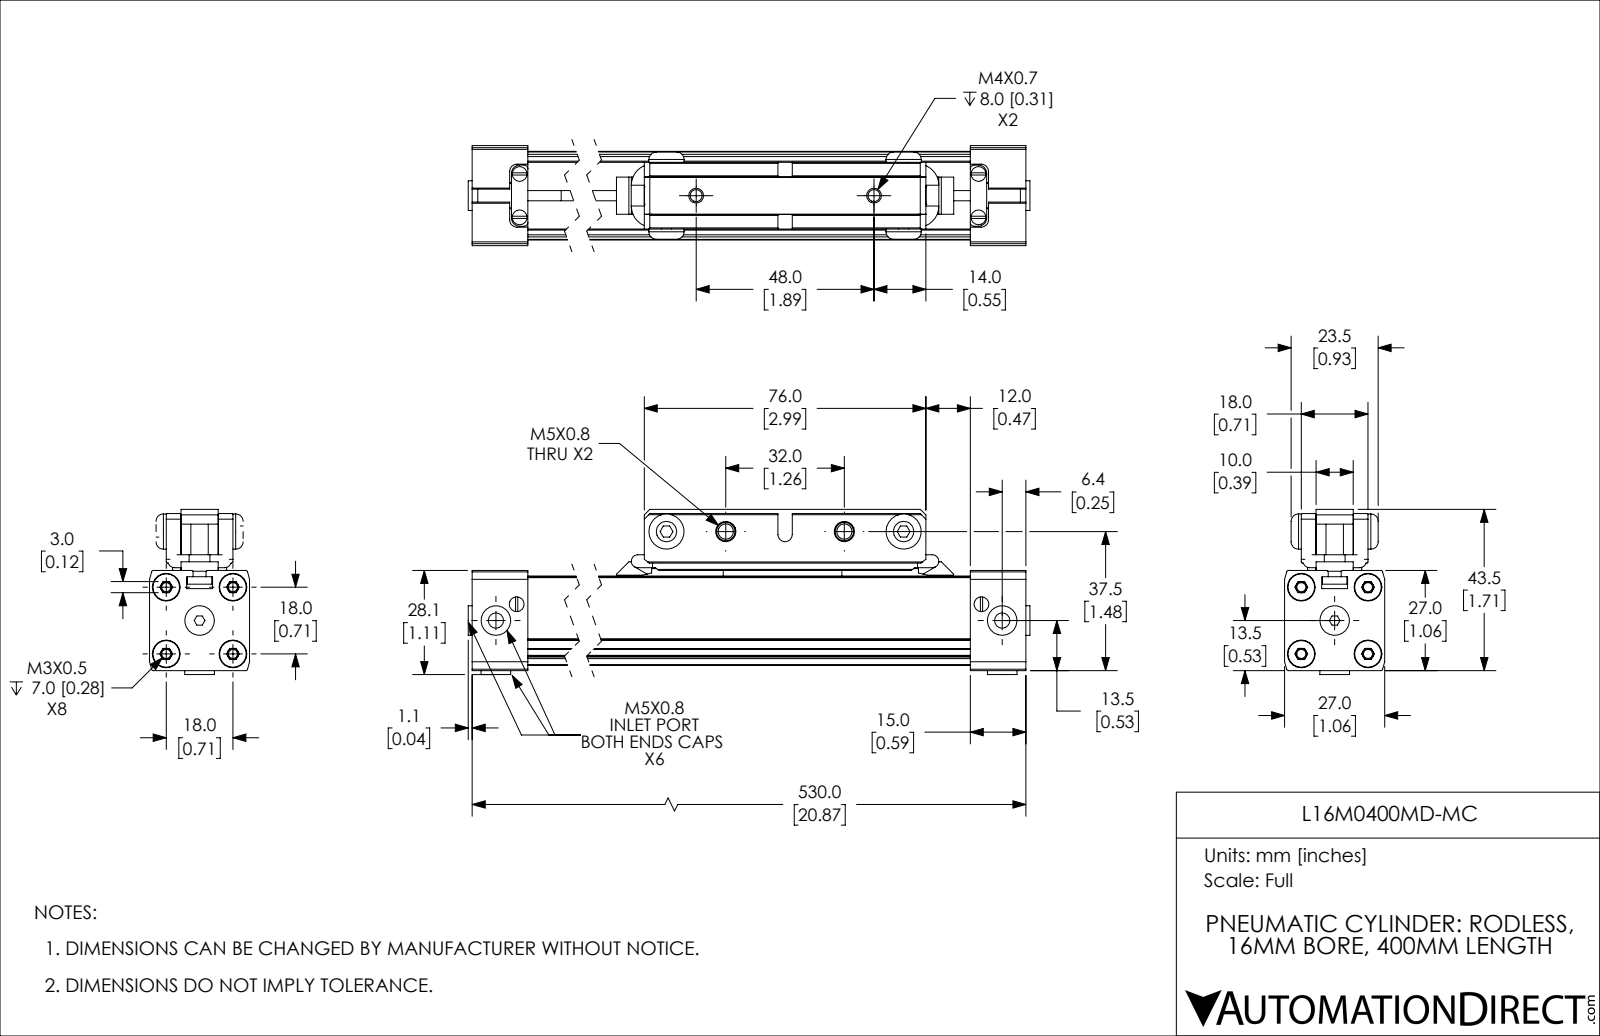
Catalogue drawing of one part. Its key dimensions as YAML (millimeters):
part_name: "L16M0400MD-MC_PISTON; L16M0400MD-MC; L16M0400MD-MC_BODY"
step_written_by: "SolidWorks 2019 (CONFIG_CONTROL_DESIGN)"
units: millimeters
bodies: {solids: 13, faces: 827, planar: 435, cylindrical: 284, other: 108}
overall_size: [532.15, 44.57, 27]
volume: 223973
surface_area: 116095
round_holes:
  - {diameter: 4.13, count: 9}
  - {diameter: 4, count: 6}
  - {diameter: 8, count: 5}
  - {diameter: 2.46, count: 4}
  - {diameter: 5.5, count: 4}
  - {diameter: 7.5, count: 4}
  - {diameter: 3.24, count: 2}
  - {diameter: 16.1, count: 1}
round_bosses_or_shafts:
  - {diameter: 7.2, count: 4}
  - {diameter: 3.5, count: 4}
  - {diameter: 5, count: 3}
  - {diameter: 3.8, count: 3}
  - {diameter: 9.5, count: 2}
  - {diameter: 16, count: 1}
partial_cylinders:
  - {radius: 0.3, count: 22}
  - {radius: 0.5, count: 14}
  - {radius: 0.25, count: 8}
  - {radius: 0.62, count: 6}
  - {radius: 1, count: 6}
  - {radius: 0.2, count: 4}
  - {radius: 0.6, count: 4}
  - {radius: 2, count: 4}
face_to_face_distances: [23.9, 24, 10.58, 13.32, 20.95, 2.95, 7.63, 10.37, 1.5, 25.5]
hole_center_spacings: [8.67, 12.73, 18, 510.83, 48, 7.12, 11.7, 11.91]
